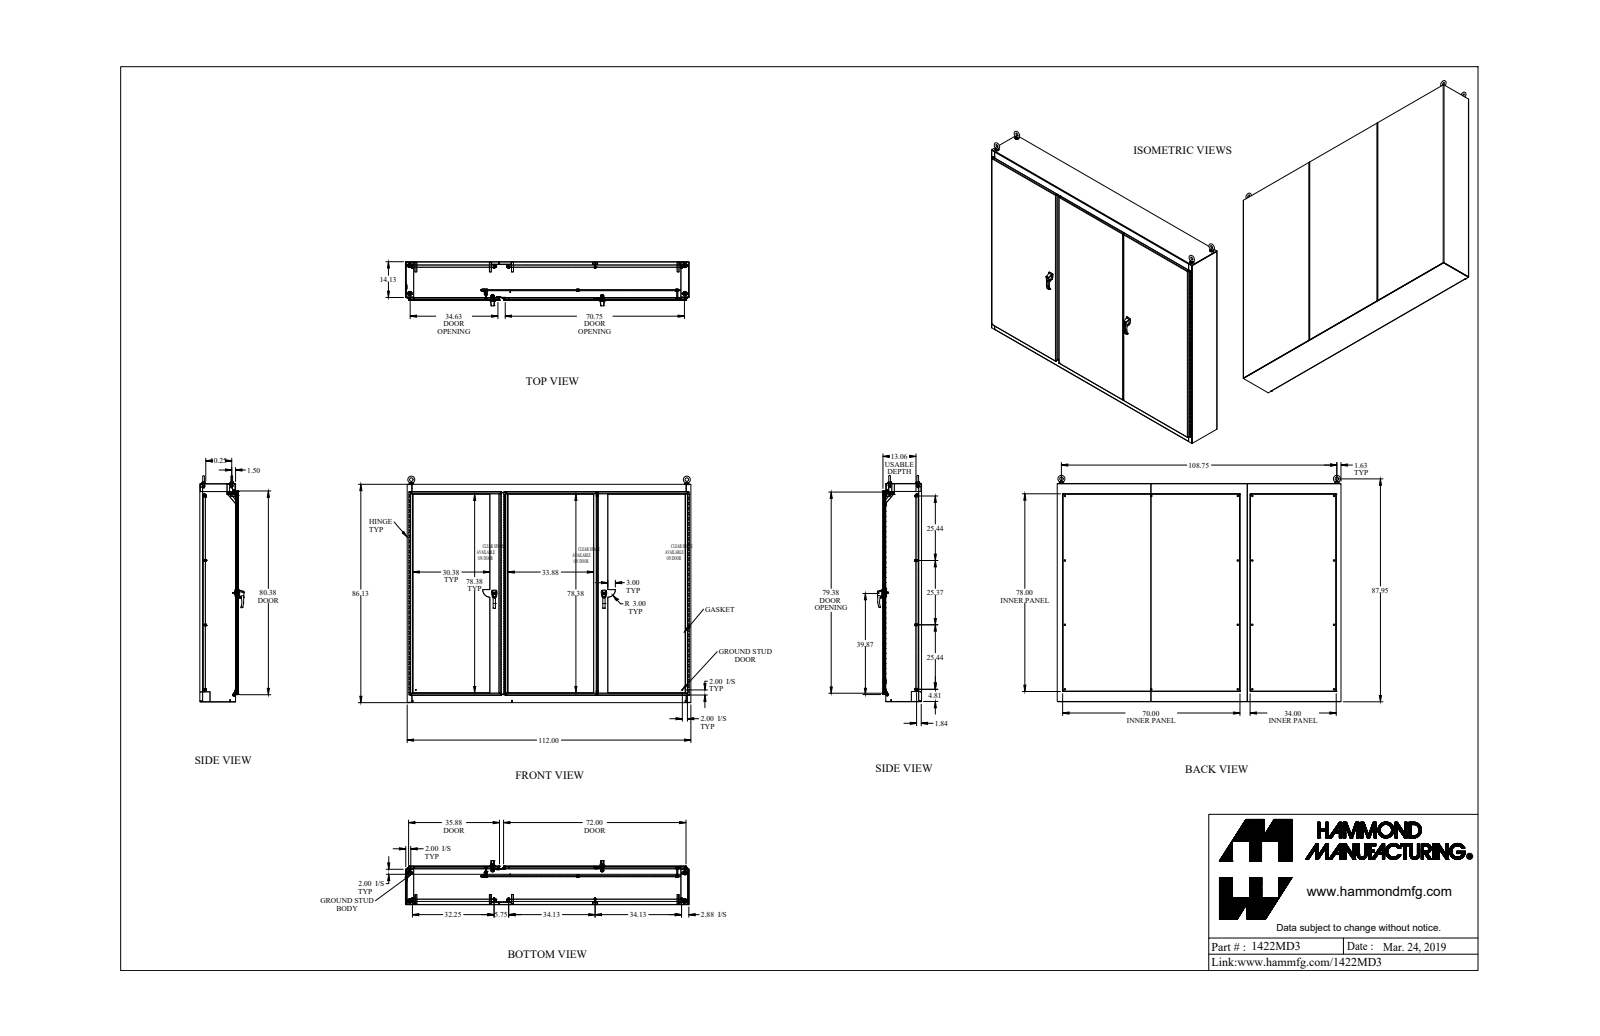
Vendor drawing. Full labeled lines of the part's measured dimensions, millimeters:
Part name (STEP PRODUCT): 1422MD3_Default
STEP written by: SolidWorks 2019 (CONFIG_CONTROL_DESIGN)
Units: millimetres
Bodies: 182 solids, 5212 faces (2313 planar, 2412 cylindrical, 487 other)
Overall size (bounding box): 2844.8 × 2280.4 × 442
Volume: 80 440 000 mm³ · Surface area: 50 010 000 mm²
Round holes (diameter × count): ⌀7.7 ×42, ⌀7.8 ×18, ⌀14.3 ×18, ⌀11.3 ×14, ⌀7.1 ×6, ⌀6.4 ×5, ⌀9.9 ×5, ⌀17.4 ×5, ⌀6.5 ×4, ⌀7.1 ×4, ⌀8 ×4, ⌀10.5 ×4
Round bosses / shafts (diameter × count): ⌀25.4 ×23, ⌀9.5 ×19, ⌀16.5 ×18, ⌀8.4 ×18, ⌀7.1 ×10, ⌀6.4 ×6, ⌀44.5 ×4, ⌀38.1 ×4
Partial cylindrical surfaces — rounded edges, fillets, slot ends (radius × count): R1.5 ×62, R4.7 ×53, R3.2 ×43, R0.4 ×32, R0.8 ×12, R1.3 ×12, R2.3 ×12, R8.1 ×12
Main face-to-face distances: 3.2, 332.7, 385.1, 52.4, 3.2, 388.3, 329.6, 55.5, 335.9, 385.1
Hole centre spacings: 152.4, 1830.9, 304.8, 1849.8, 457.2, 1880.9, 609.6, 1923.7
